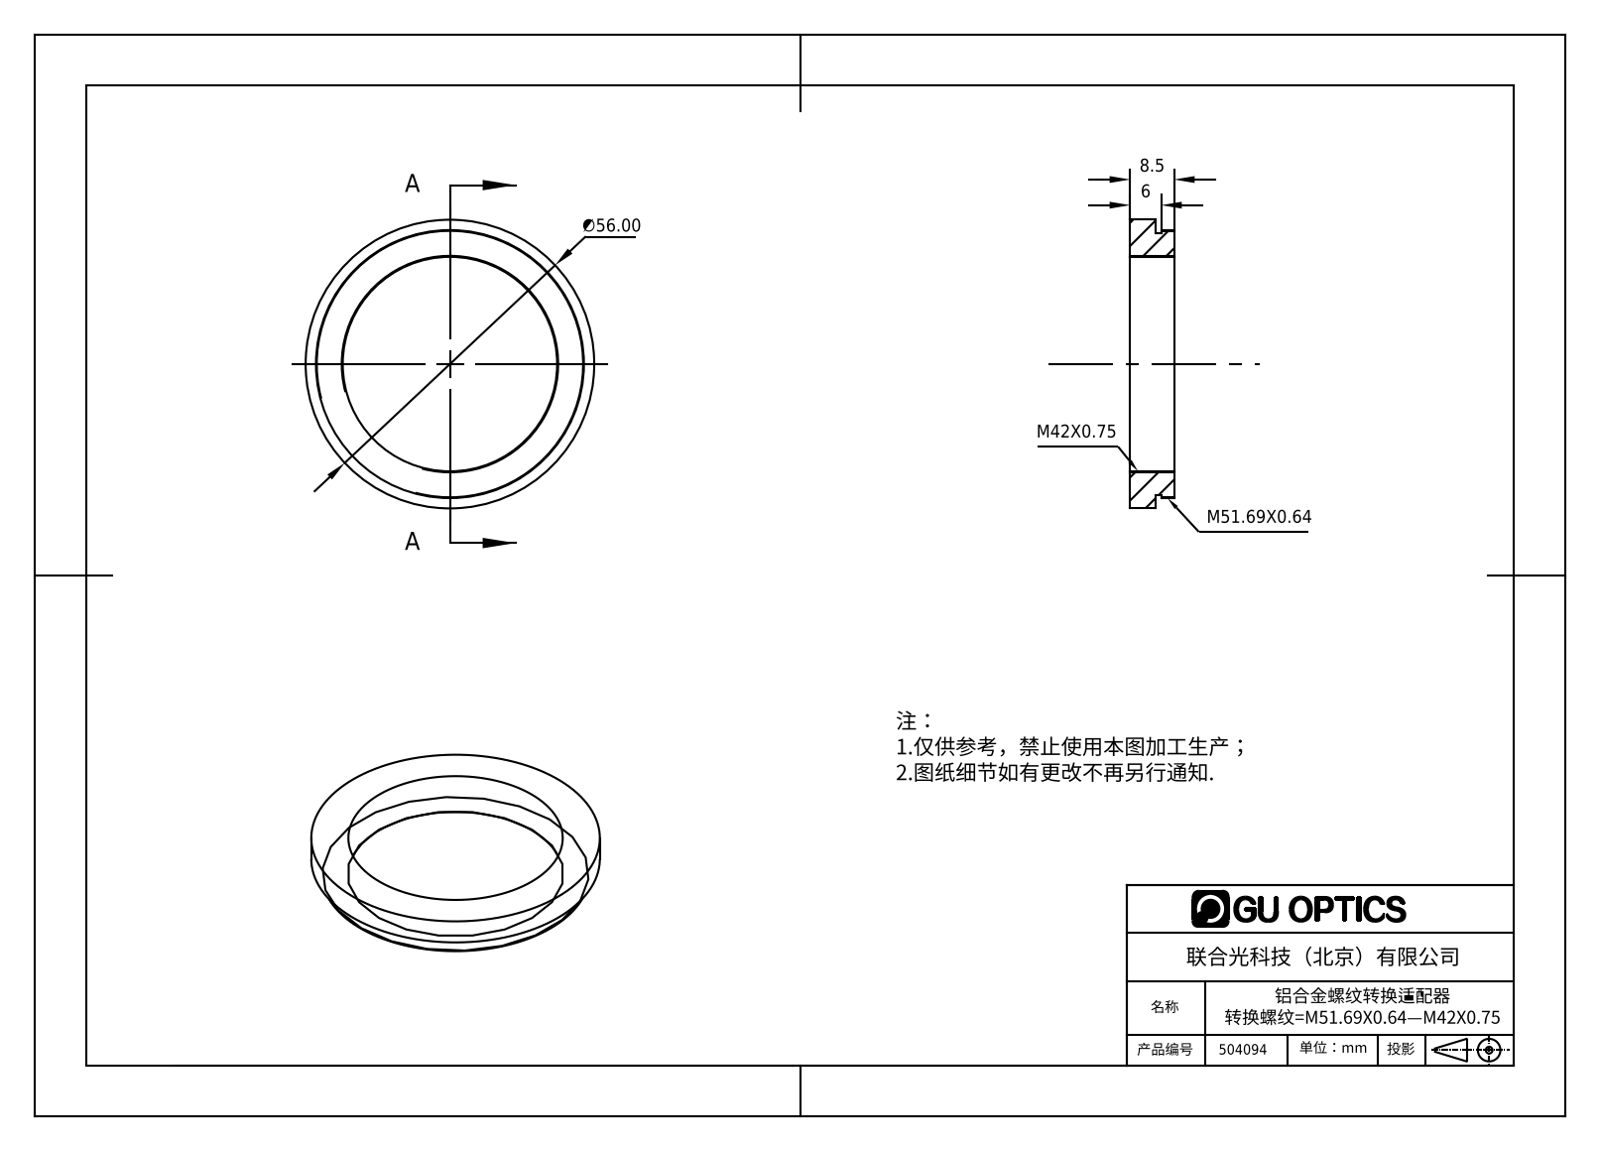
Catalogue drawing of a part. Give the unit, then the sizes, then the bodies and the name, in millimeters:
Units: millimetres
Overall size (bounding box): 56 × 56 × 8.5
Round holes (diameter × count): ⌀41.6 ×1
Round bosses / shafts (diameter × count): ⌀56 ×1, ⌀52 ×1, ⌀50.8 ×1
Main face-to-face distances: 8.5, 3.5, 5, 2.5, 1, 6
Volume: 8 098 mm³ · Surface area: 4 960 mm²
Bodies: 1 solid, 12 faces (4 planar, 8 cylindrical, 0 other)
Part name (STEP PRODUCT): 504094
STEP written by: SolidWorks 2016 (AUTOMOTIVE_DESIGN)
